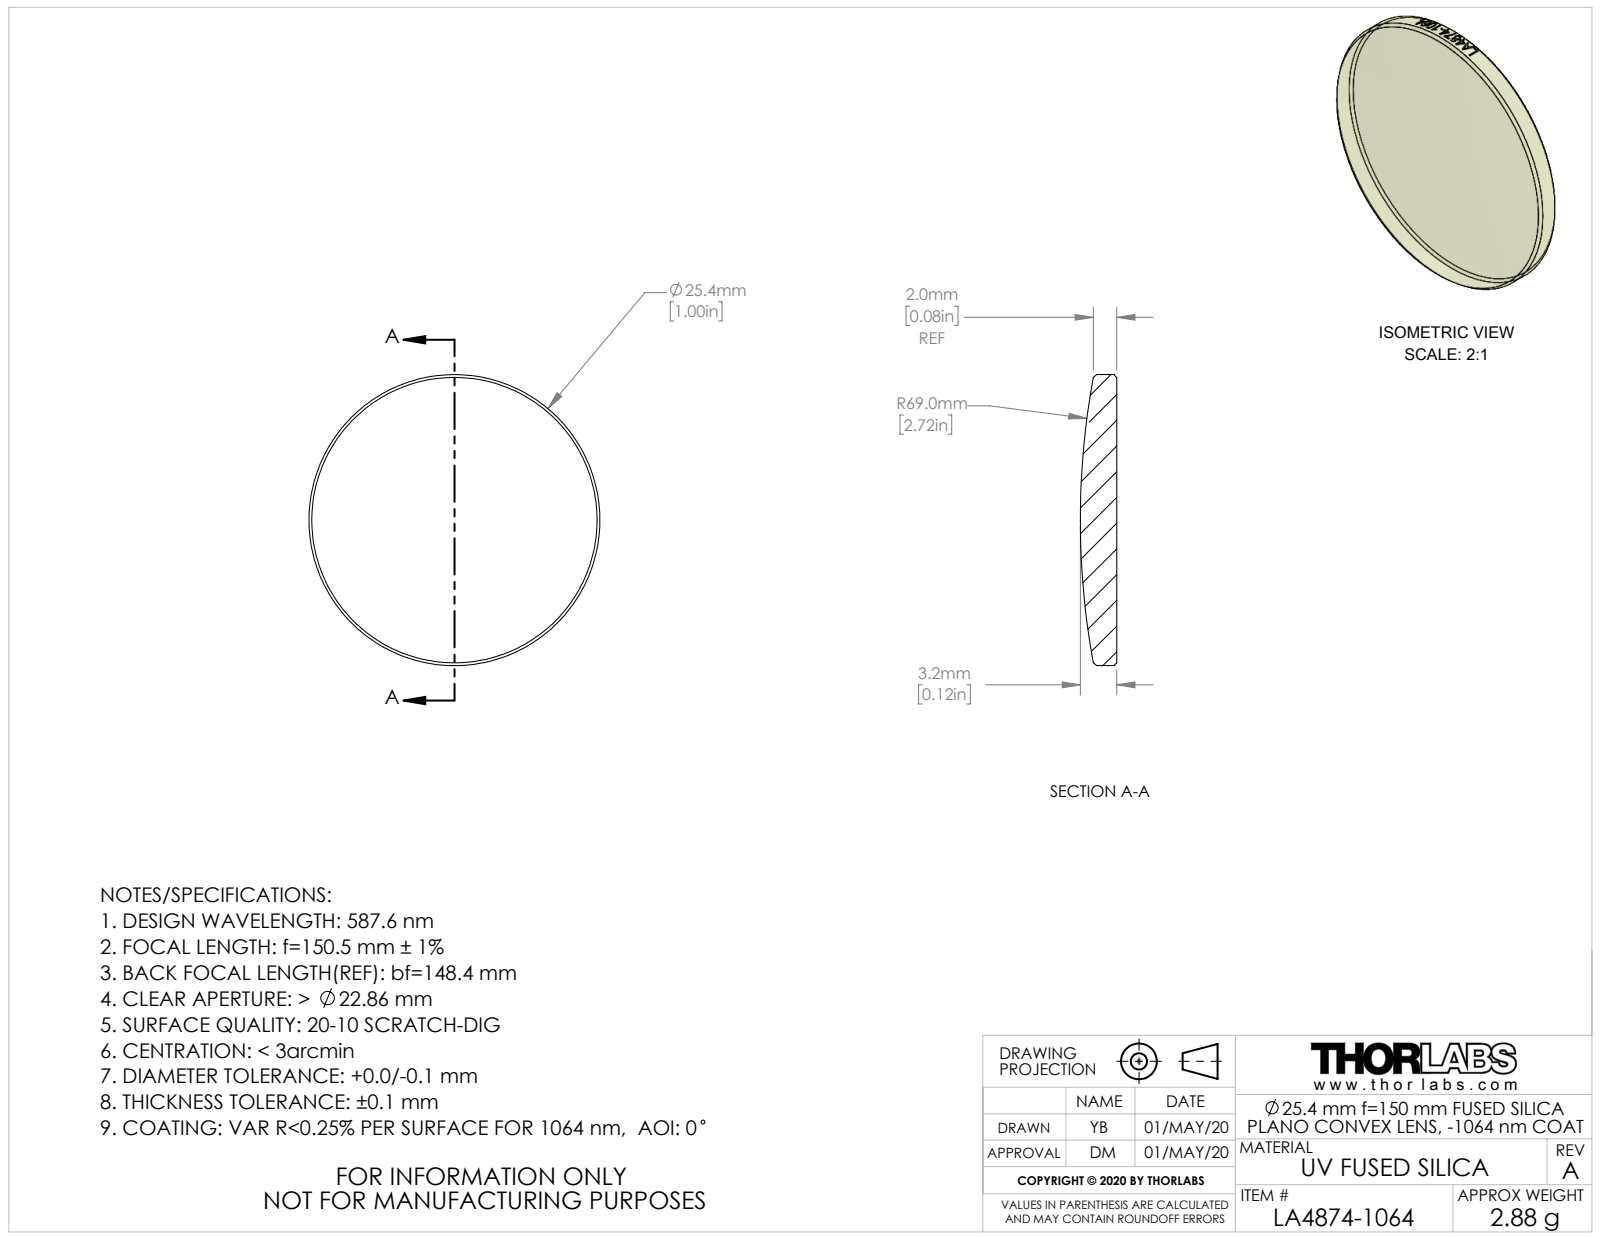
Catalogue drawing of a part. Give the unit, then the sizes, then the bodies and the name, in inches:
Units: inches
Overall size (bounding box): 1 × 1 × 0.125
Round bosses / shafts (diameter × count): ⌀1 ×1
Volume: 0.08 in³ · Surface area: 1.792 in²
Bodies: 1 solid, 30 faces (1 planar, 23 cylindrical, 6 other)
Part name (STEP PRODUCT): CTN015543-E0W
STEP written by: SolidWorks 2018 (AUTOMOTIVE_DESIGN)
